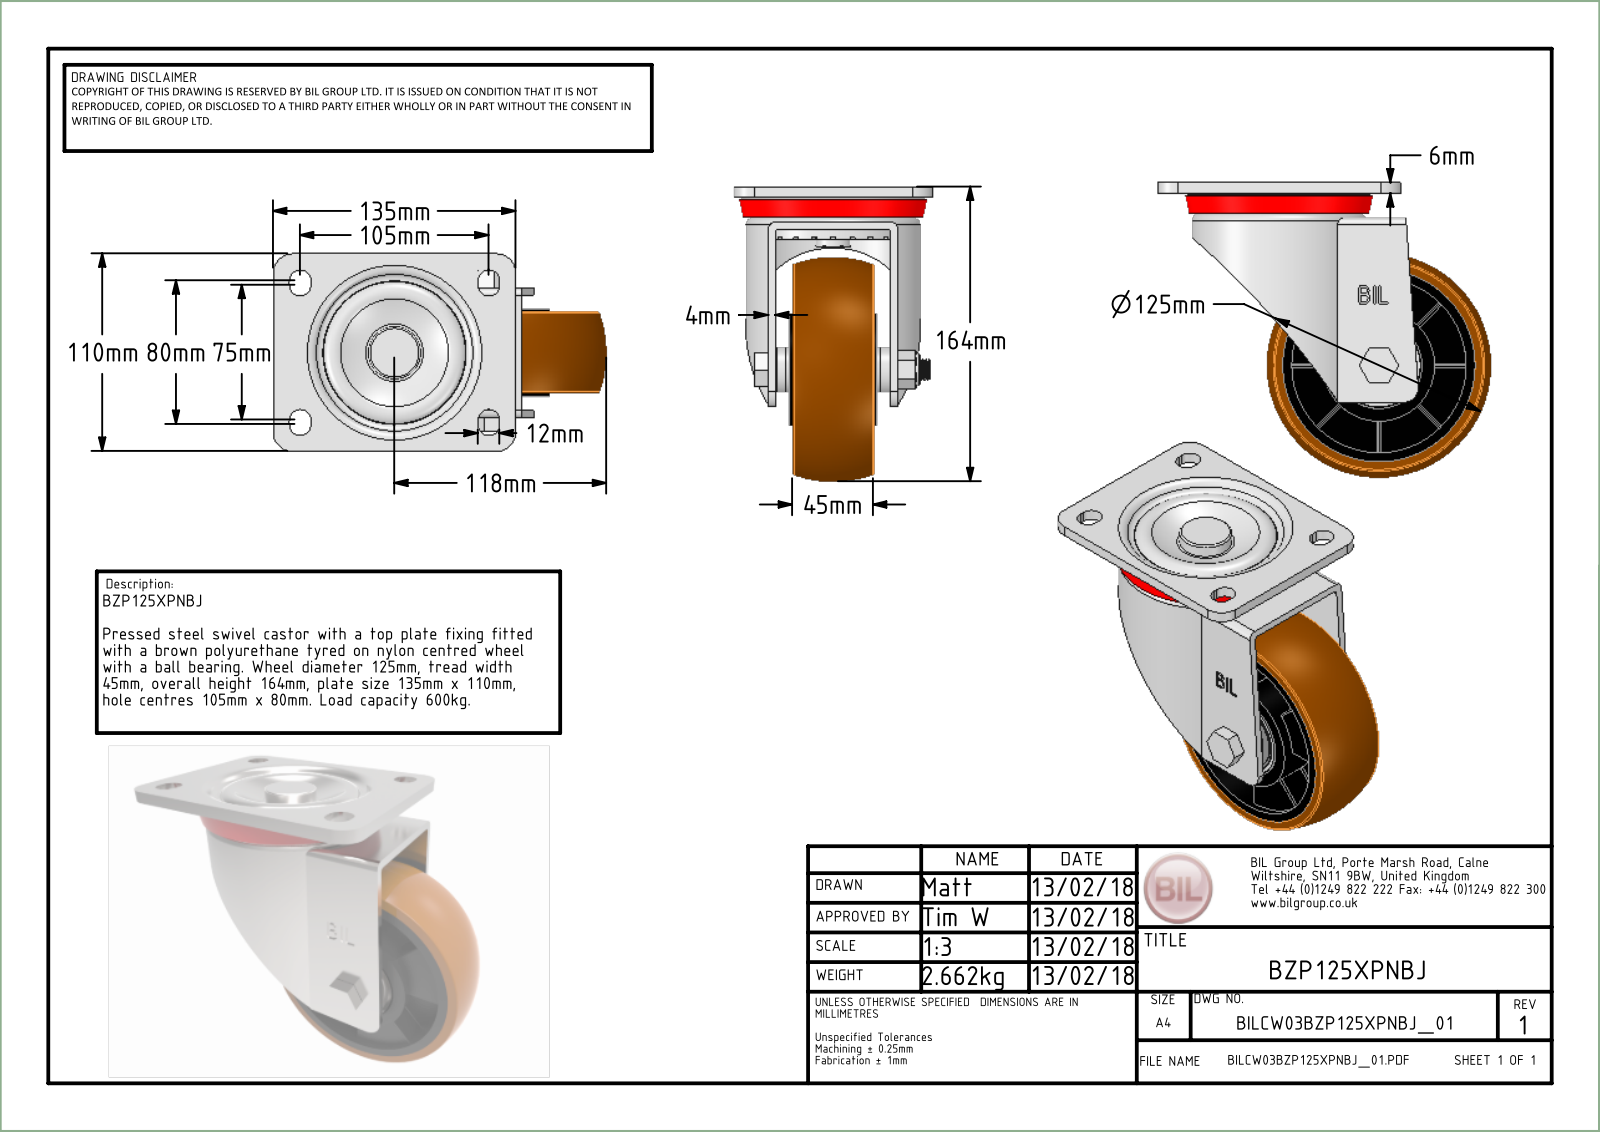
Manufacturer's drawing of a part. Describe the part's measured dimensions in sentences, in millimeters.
The part is named "BZP125XPNBJ v4; BZP125AS - 63 v1; BZP125AS v1 (1); ZINC PLATED, PRESSED STEEL TOP PLATE (1) (+8 more)". Its 3-D file was written by "Autodesk Translation Framework v14.10.0.0 (AUTOMOTIVE_DESIGN)". It is 40 solids with 1395 faces: 661 planar, 238 cylindrical and 496 other. Overall it measures 185.5 by 164 by 110 millimeters. Its volume is 661 521 cubic millimeters and its surface area 274 808 square millimeters. Round holes: 2 of diameter 30, 1 of diameter 12, 1 of diameter 12.2, 1 of diameter 12.5, 1 of diameter 12.75, 1 of diameter 14, 1 of diameter 19, 1 of diameter 20, 1 of diameter 28.5, 1 of diameter 30.8, 1 of diameter 40, 1 of diameter 40.3. Round bosses or shafts: 1 of diameter 105.5, 1 of diameter 96, 1 of diameter 83, 1 of diameter 62, 1 of diameter 50, 1 of diameter 40.8, 1 of diameter 31.3, 1 of diameter 29. Partial cylindrical surfaces (rounded edges, fillets, slot ends): 20 of radius 0.5, 8 of radius 9.09, 4 of radius 0.47, 4 of radius 0.9, 4 of radius 14, 2 of radius 0.89, 2 of radius 0.89, 2 of radius 4. The main face-to-face distances are 7, 9, 4, 14, 5, 13, 58, 35, 6, 2.
